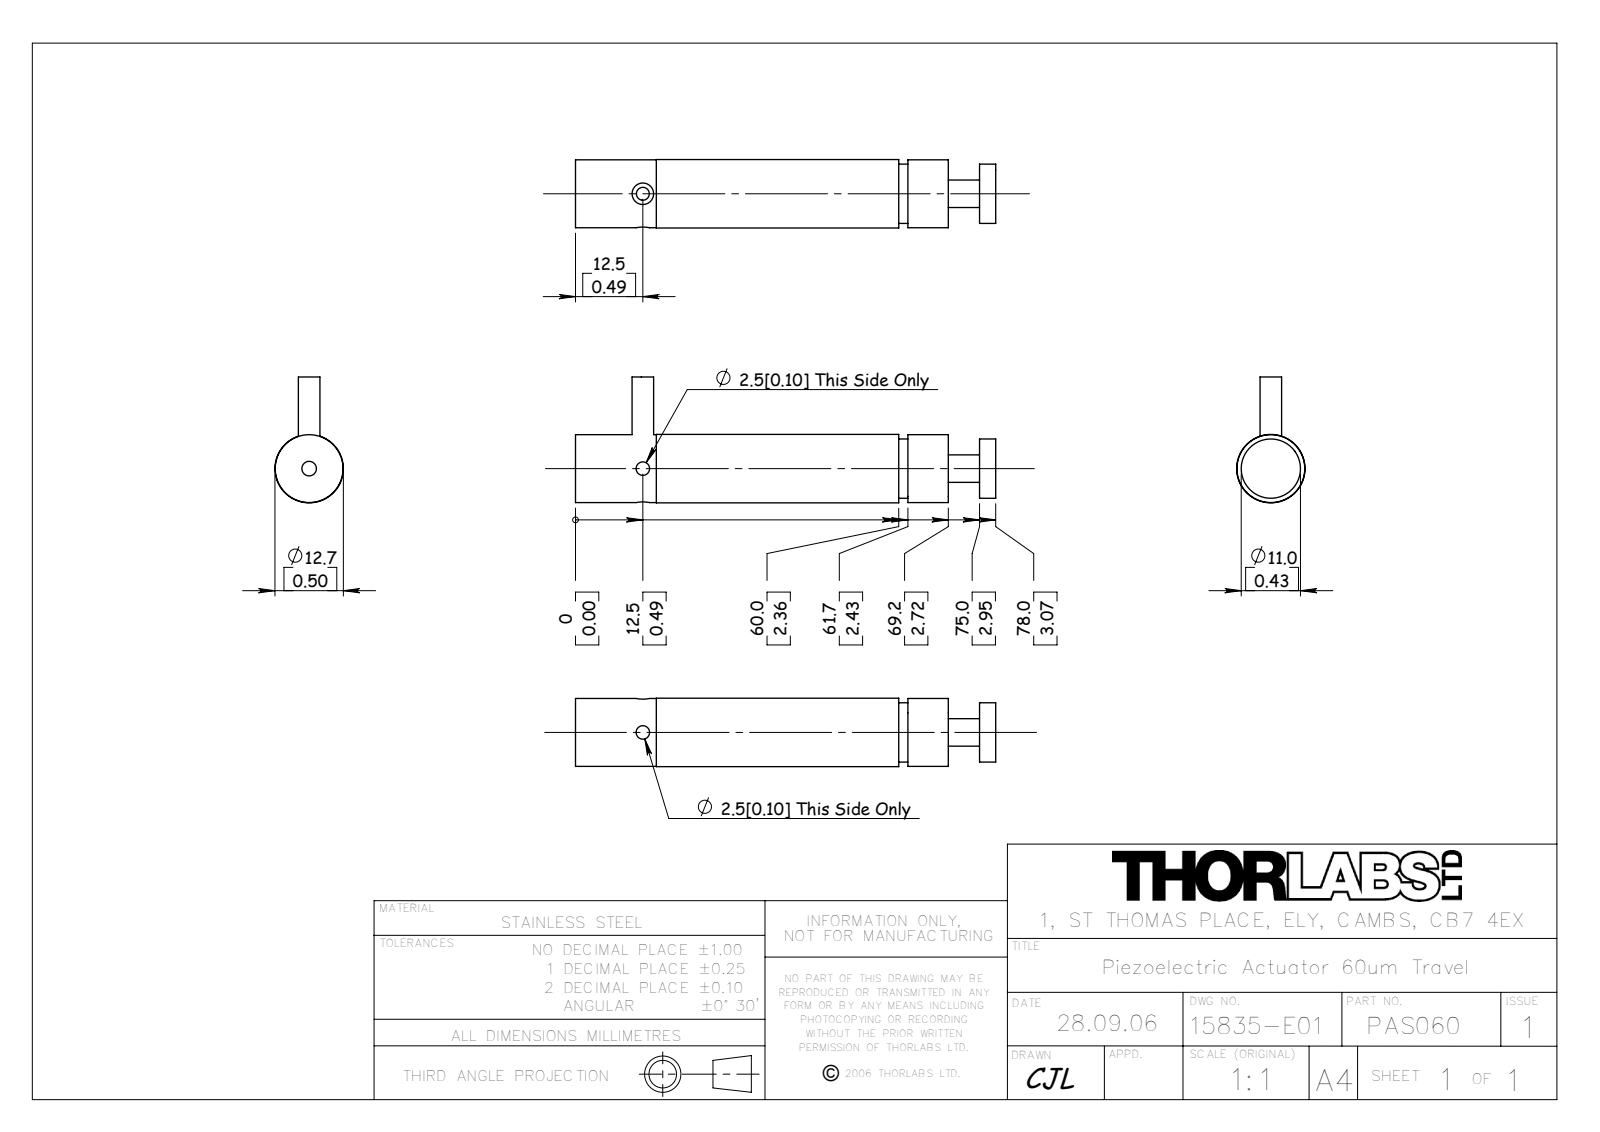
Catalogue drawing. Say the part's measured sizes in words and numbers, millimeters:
The part is named "15835-E0W". Its 3-D file was written by "SolidWorks 2007 (AUTOMOTIVE_DESIGN)". It is 0 solids with 39 faces: 11 planar, 28 cylindrical and 0 other. Overall it measures 78 by 23.35 by 12.7 millimeters. Round holes: 2 of diameter 2.5, 1 of diameter 2.4, 1 of diameter 2.71, 1 of diameter 5.3, 1 of diameter 9.55, 1 of diameter 11.4. Round bosses or shafts: 1 of diameter 12.7, 1 of diameter 12.6, 1 of diameter 11, 1 of diameter 5.1, 1 of diameter 4. The main face-to-face distances are 69.2, 8.8, 78, 3, 5.8, 75, 15, 60, 68, 65.
